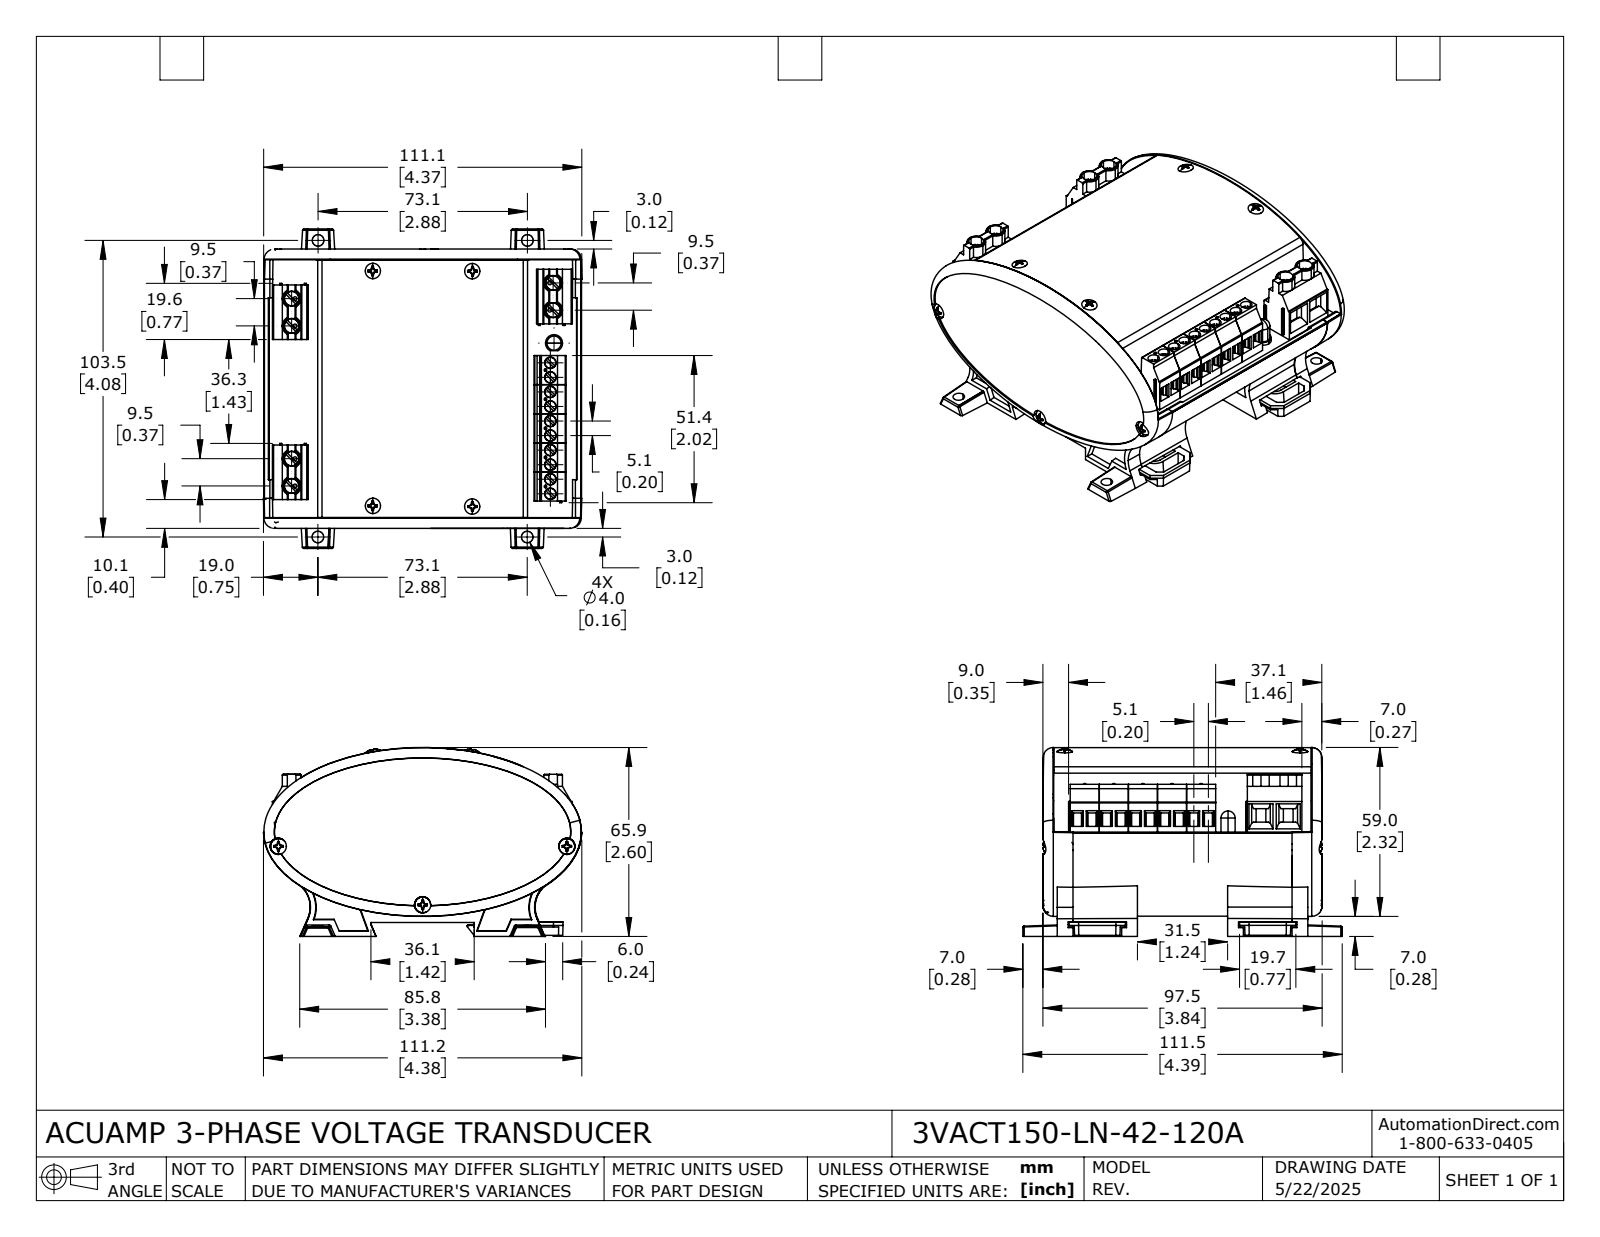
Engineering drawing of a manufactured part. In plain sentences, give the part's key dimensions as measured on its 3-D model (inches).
The part is named "3VACT150-LN-42-120A". Its 3-D file was written by "SolidWorks 2024 (AUTOMOTIVE_DESIGN)". It is 26 solids with 2967 faces: 1482 planar, 844 cylindrical and 641 other. Overall it measures 7.429 by 4.374 by 2.597 inches. Its volume is 11.76 cubic inches and its surface area 284.7 square inches. Round holes: 12 of diameter 0.05, 10 of diameter 0.157, 6 of diameter 0.08, 6 of diameter 0.205, 4 of diameter 0.126, 3 of diameter 0.111, 3 of diameter 0.28. Round bosses or shafts: 16 of diameter 0.051, 10 of diameter 0.15, 10 of diameter 0.112, 10 of diameter 0.067, 6 of diameter 0.197, 4 of diameter 0.018, 1 of diameter 0.234, 1 of diameter 0.194. Partial cylindrical surfaces (rounded edges, fillets, slot ends): 38 of radius 0.006, 20 of radius 0.039, 17 of radius 0.02, 12 of radius 0.008, 8 of radius 0.012, 6 of radius 0.01, 6 of radius 0.128, 4 of radius 0.018. The main face-to-face distances are 0.063, 0.128, 6.709, 0.084, 6.838, 6.581, 0.394, 6.444, 0.266, 6.315. The hole center spacings are 0.2, 0.4, 0.6, 0.8, 1, 1.2, 0.2, 0.2.
